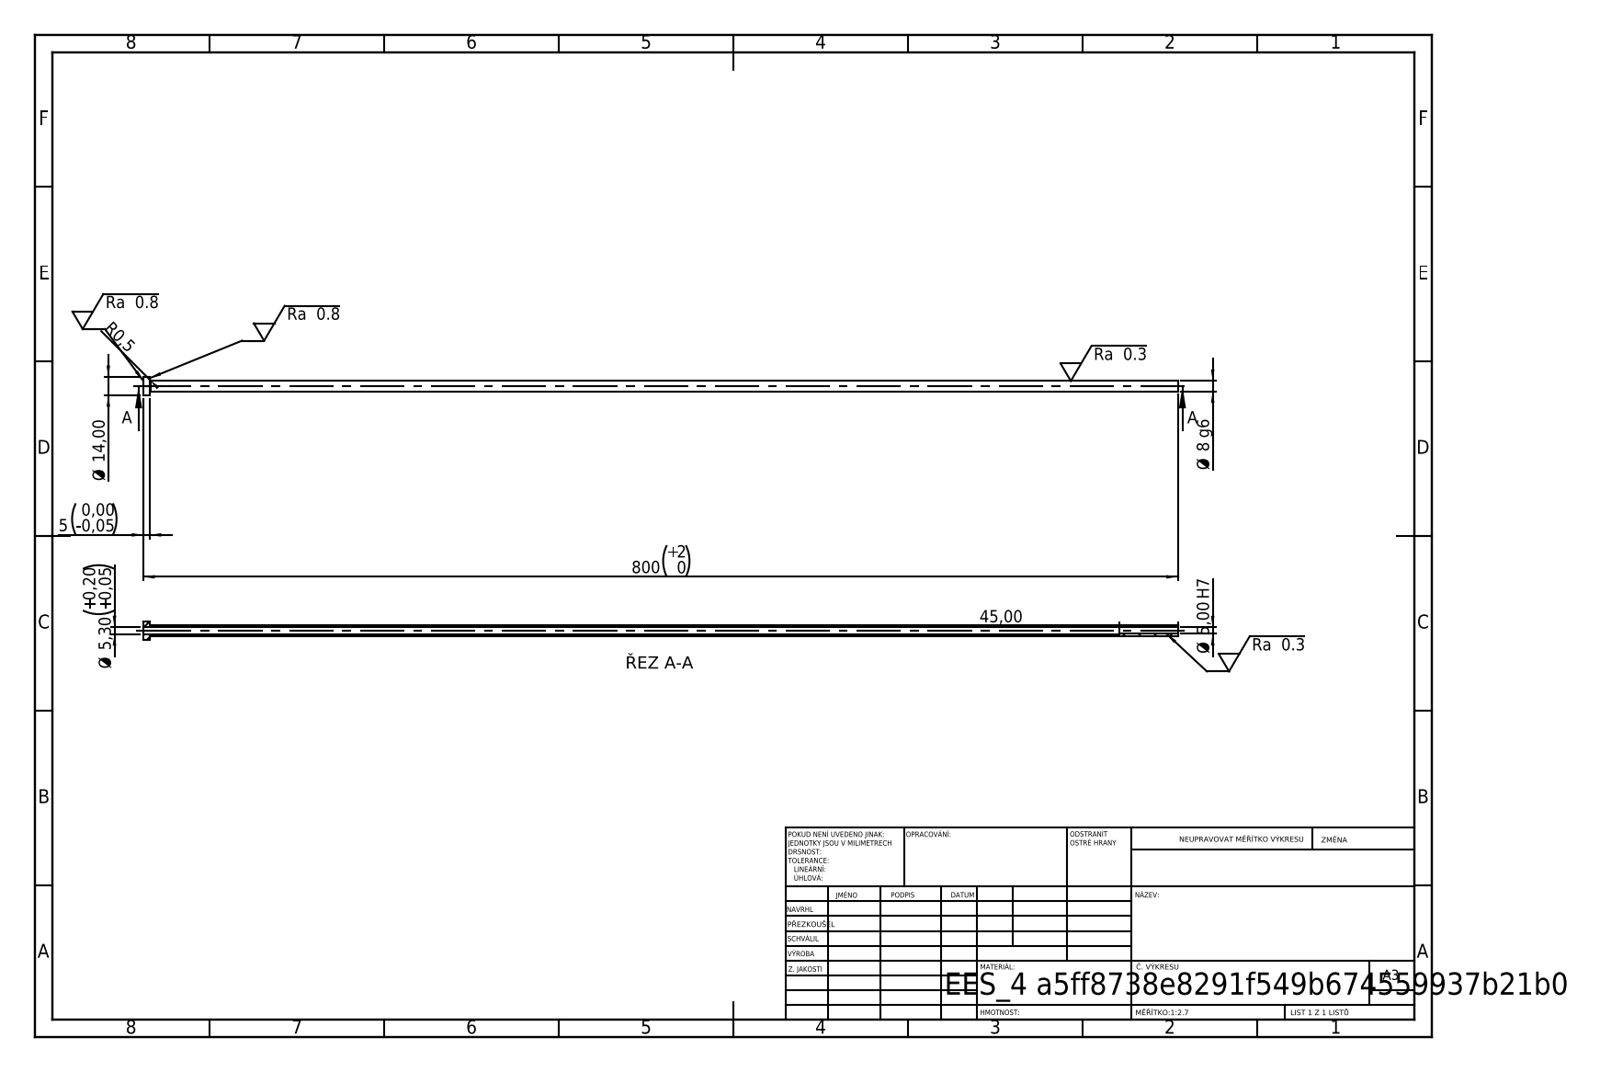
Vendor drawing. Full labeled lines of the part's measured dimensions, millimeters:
STEP written by: SolidWorks 2019 (CONFIG_CONTROL_DESIGN)
Units: millimetres
Bodies: 1 solid, 14 faces (4 planar, 8 cylindrical, 2 other)
Overall size (bounding box): 800 × 14 × 14
Volume: 23 192 mm³ · Surface area: 33 742 mm²
Round holes (diameter × count): ⌀5 ×1, ⌀5.3 ×1
Round bosses / shafts (diameter × count): ⌀14 ×1, ⌀8 ×1
Main face-to-face distances: 5, 800, 795, 755, 750, 45
